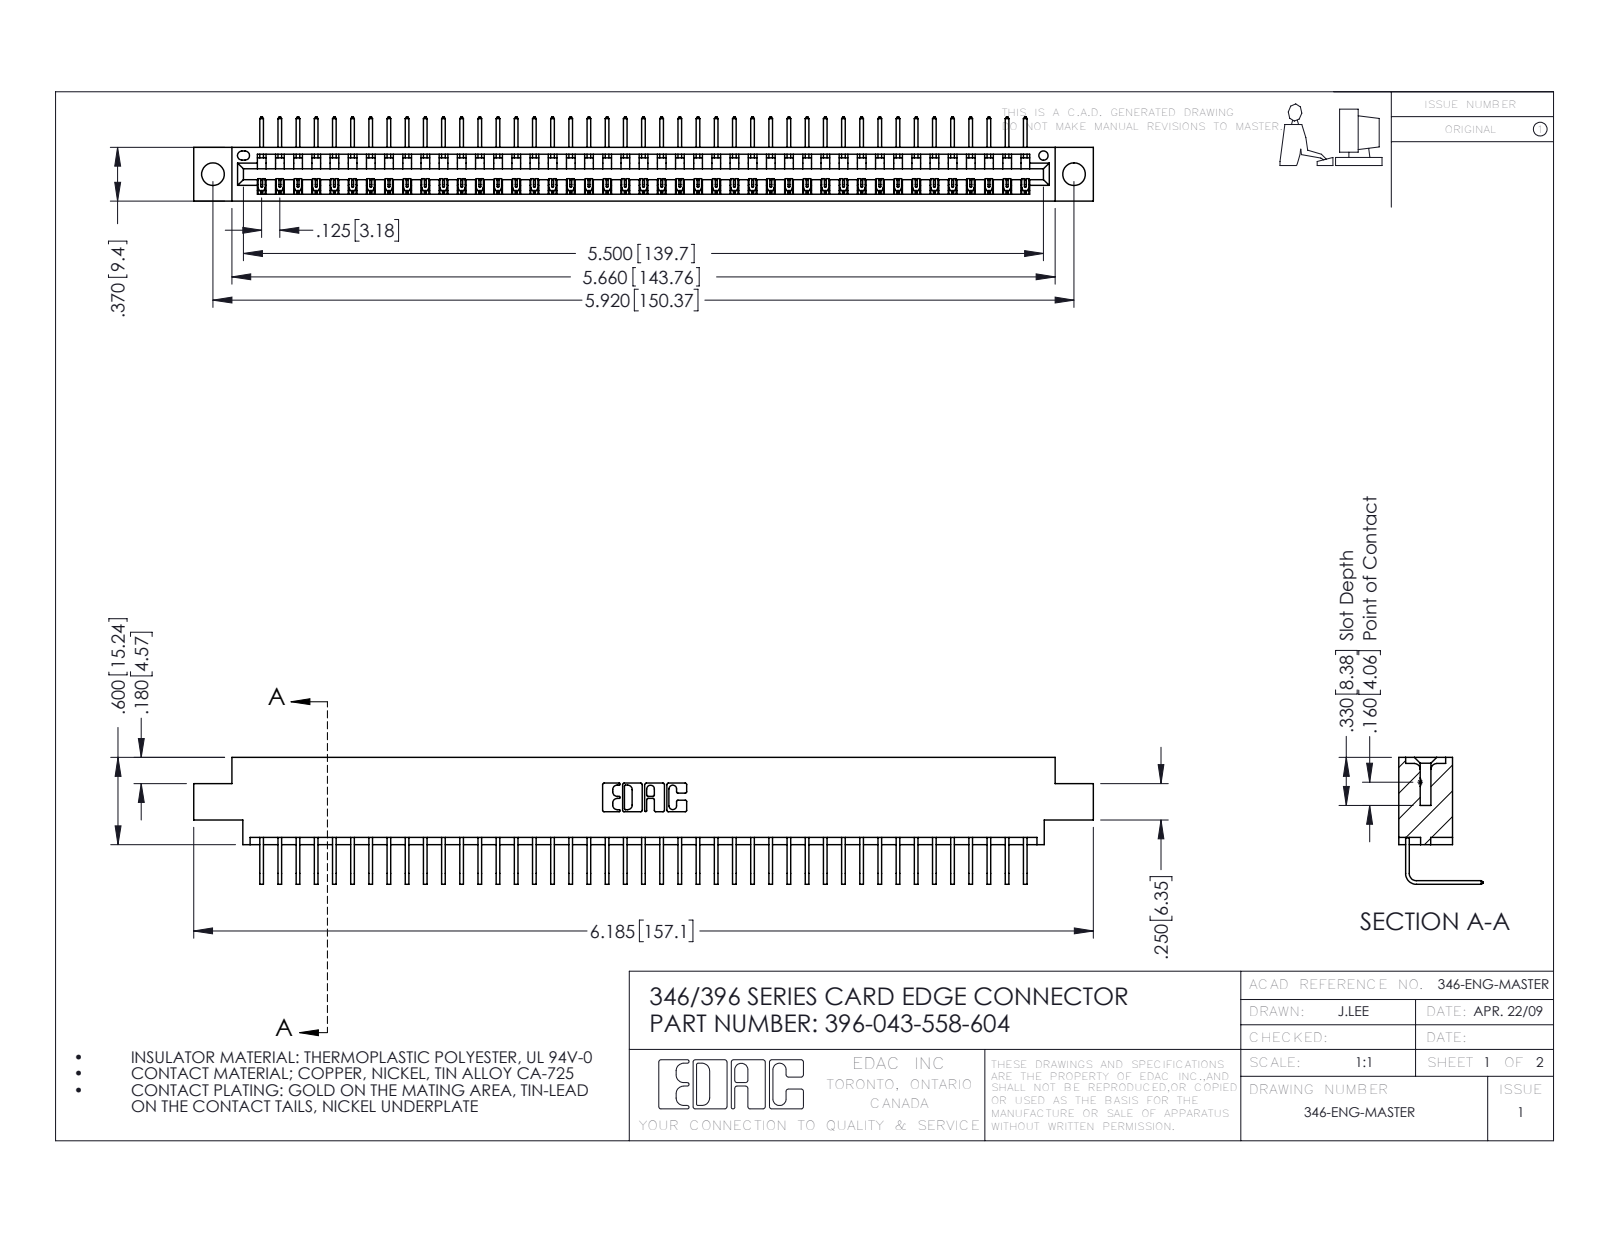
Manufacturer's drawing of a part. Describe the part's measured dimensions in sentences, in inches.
The part is named "345-292-001_558 Tail - 2; 396-043-558-604; 346 Part_0.170 Offset - 0.156 Dia-TH". Its 3-D file was written by "SolidWorks 2016 (CONFIG_CONTROL_DESIGN)". It is 44 solids with 2706 faces: 1886 planar, 820 cylindrical and 0 other. Overall it measures 6.185 by 0.873 by 0.58 inches. Its volume is 0.912 cubic inches and its surface area 30.24 square inches. Round holes: 2 of diameter 0.156, 1 of diameter 0.064. Partial cylindrical surfaces (rounded edges, fillets, slot ends): 86 of radius 0.006, 22 of radius 0.01, 6 of radius 0.007, 6 of radius 0.031, 3 of radius 0.026, 2 of radius 0.031, 2 of radius 0.04, 1 of radius 0.014. The main face-to-face distances are 0.322, 0.048, 0.37, 0.25, 0.298, 0.025, 0.072, 0.148, 0.222, 0.1. The hole center spacings are 0.246, 5.711, 5.92.
